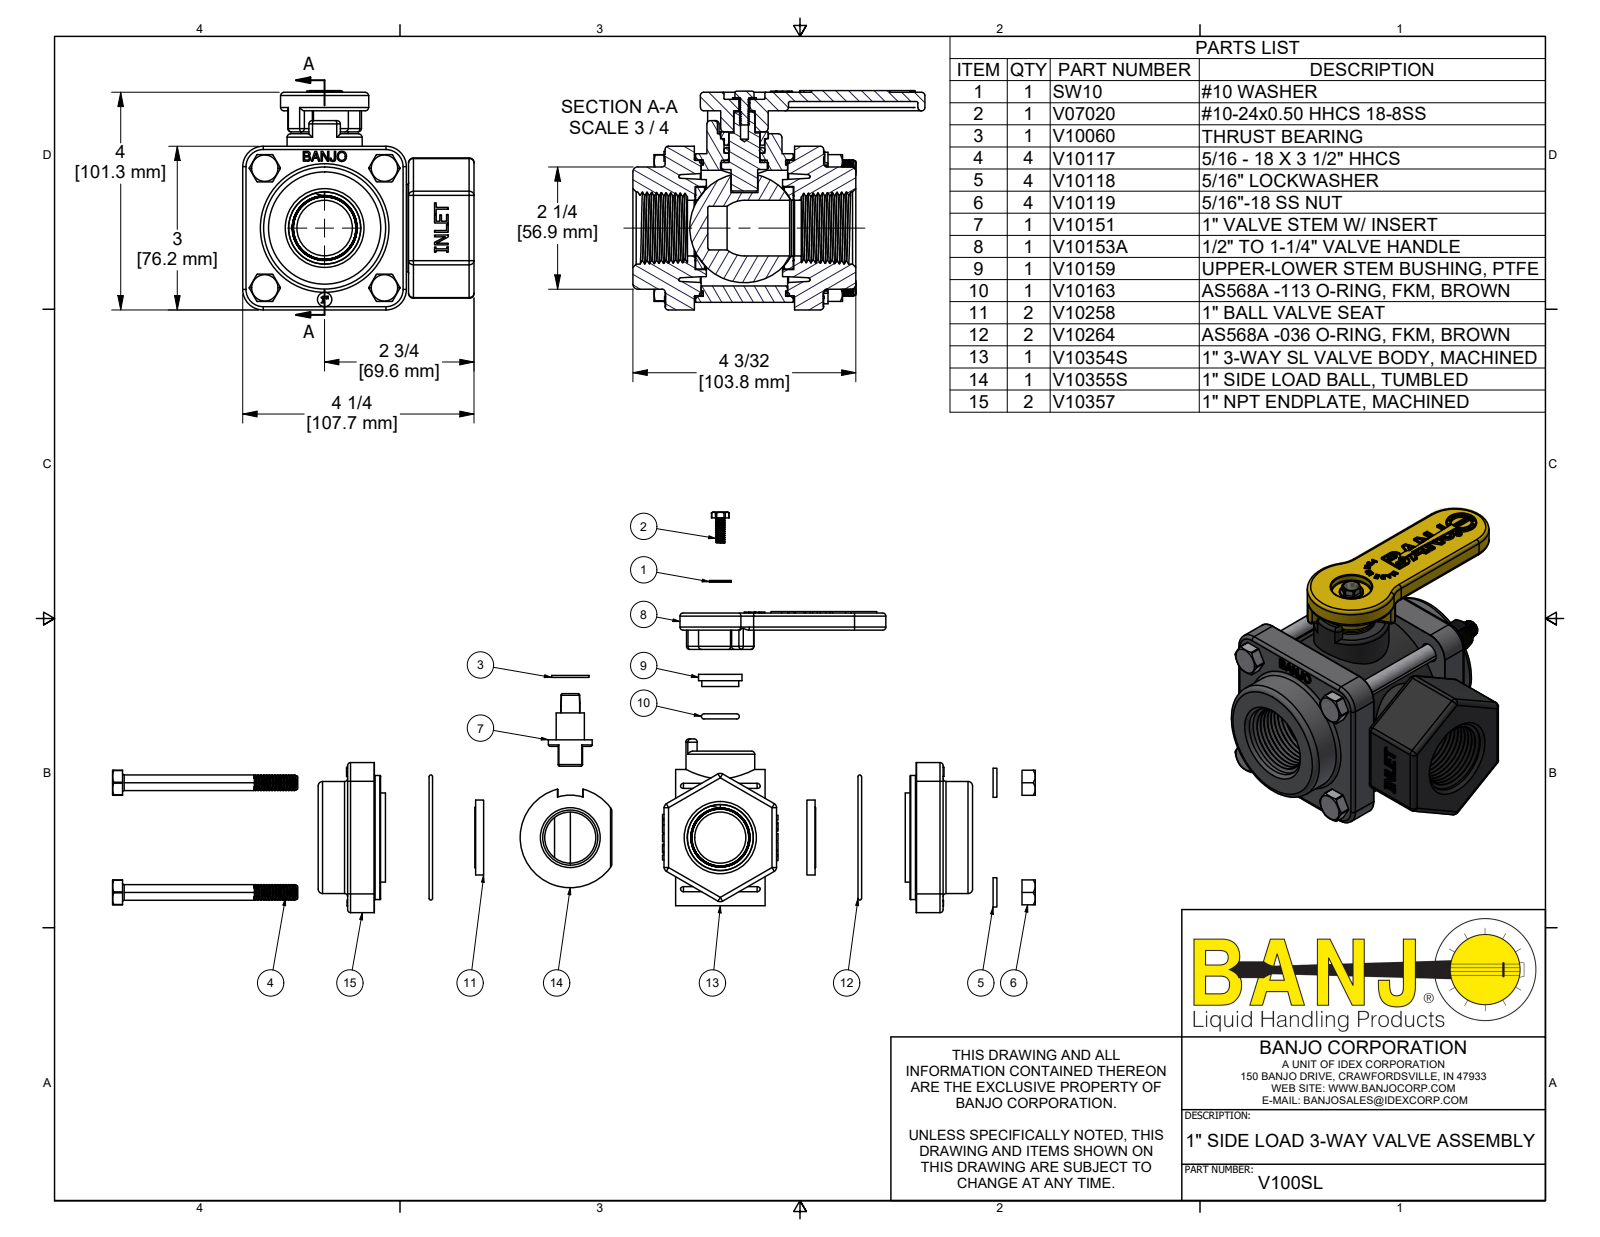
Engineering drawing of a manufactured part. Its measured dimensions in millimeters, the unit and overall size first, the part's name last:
Units: millimetres
Overall size (bounding box): 136 × 107.7 × 102
Round holes (diameter × count): ⌀6.4 ×4, ⌀8.2 ×4, ⌀9.3 ×4, ⌀25.9 ×2, ⌀2.3 ×1, ⌀3.7 ×1, ⌀5.1 ×1, ⌀5.2 ×1, ⌀6.6 ×1, ⌀9.6 ×1, ⌀13.5 ×1, ⌀14.3 ×1
Round bosses / shafts (diameter × count): ⌀6.8 ×60, ⌀14.8 ×4, ⌀8 ×4, ⌀69.2 ×1, ⌀63 ×1, ⌀58.5 ×1, ⌀56.9 ×1, ⌀45.2 ×1
Partial cylindrical surfaces — rounded edges, fillets, slot ends (radius × count): R1.5 ×54, R0.8 ×24, R2.3 ×18, R0.8 ×12, R3.4 ×8, R9.5 ×5, R0.4 ×4, R7.2 ×4
Main face-to-face distances: 13.6, 60.3, 3.2, 16.8, 57.1, 43.5, 76.2, 31.8, 73.9, 57.2
Hole centre spacings: 39.4, 55.7, 28.4, 67.2, 78.7, 9.2, 33.3, 65.3
Volume: 424 400 mm³ · Surface area: 142 700 mm²
Bodies: 28 solids, 3954 faces (1903 planar, 622 cylindrical, 1429 other)
Part name (STEP PRODUCT): V100SL; V10264; V10258; V10151 (+8 more)
STEP written by: Autodesk Inventor 2022 (AUTOMOTIVE_DESIGN)
